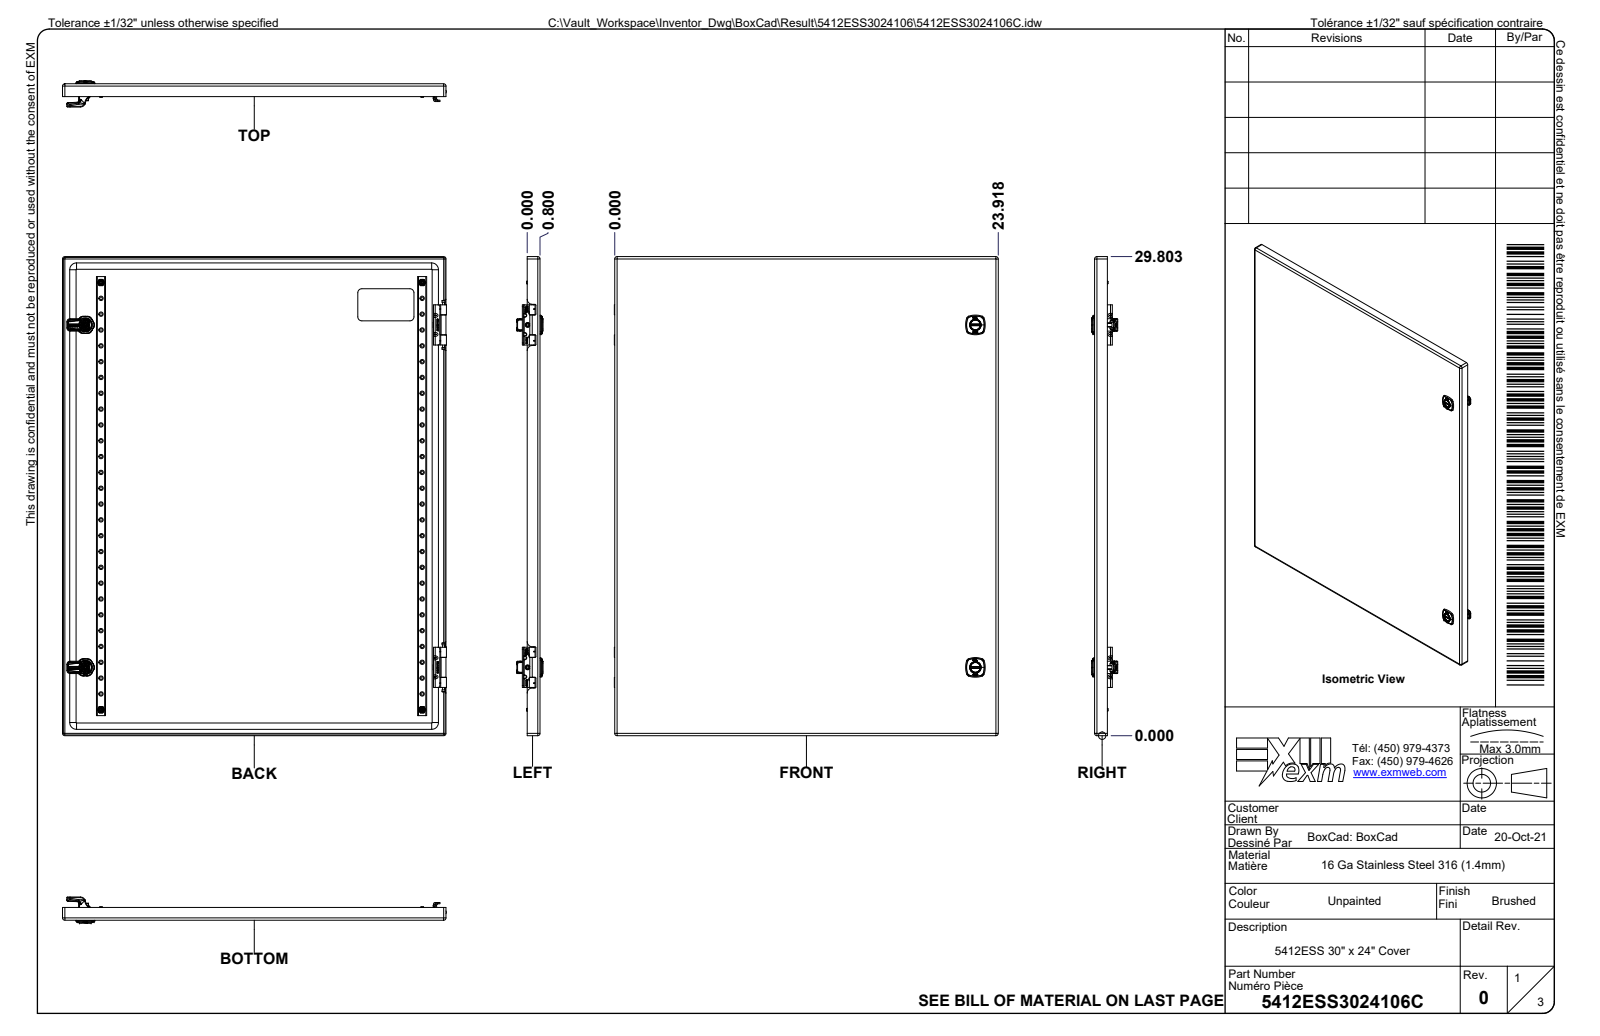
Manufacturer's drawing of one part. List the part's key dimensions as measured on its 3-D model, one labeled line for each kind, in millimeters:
Part name (STEP PRODUCT): 5412ESS3024106; 5412ESS3024106B; 5412ESS3024106B-P; STK-Q-16020 (+8 more)
STEP written by: Autodesk Inventor 2024 (AUTOMOTIVE_DESIGN)
Units: millimetres
Bodies: 64 solids, 9382 faces (3057 planar, 1987 cylindrical, 4338 other)
Overall size (bounding box): 762 × 609.6 × 287.2
Volume: 3 784 000 mm³ · Surface area: 4 701 000 mm²
Round holes (diameter × count): ⌀4.2 ×52, ⌀0.8 ×9, ⌀5.1 ×8, ⌀8 ×8, ⌀7.4 ×6, ⌀7.9 ×6, ⌀1.1 ×4, ⌀5 ×4, ⌀6.8 ×4, ⌀6.9 ×4, ⌀9.9 ×4, ⌀6 ×2
Round bosses / shafts (diameter × count): ⌀6 ×52, ⌀5.9 ×9, ⌀0.8 ×9, ⌀1 ×8, ⌀18.2 ×4, ⌀9.5 ×4, ⌀7.9 ×4, ⌀6.7 ×4
Partial cylindrical surfaces — rounded edges, fillets, slot ends (radius × count): R0.5 ×106, R0.2 ×68, R1 ×62, R0.3 ×34, R0.8 ×34, R0.3 ×28, R2.1 ×24, R3.2 ×20
Main face-to-face distances: 1.3, 281.5, 280.1, 282.8, 23.5, 22.2, 257.9, 259.3, 2.7, 26.2
Hole centre spacings: 25, 50, 75, 100, 125, 150, 175, 200
